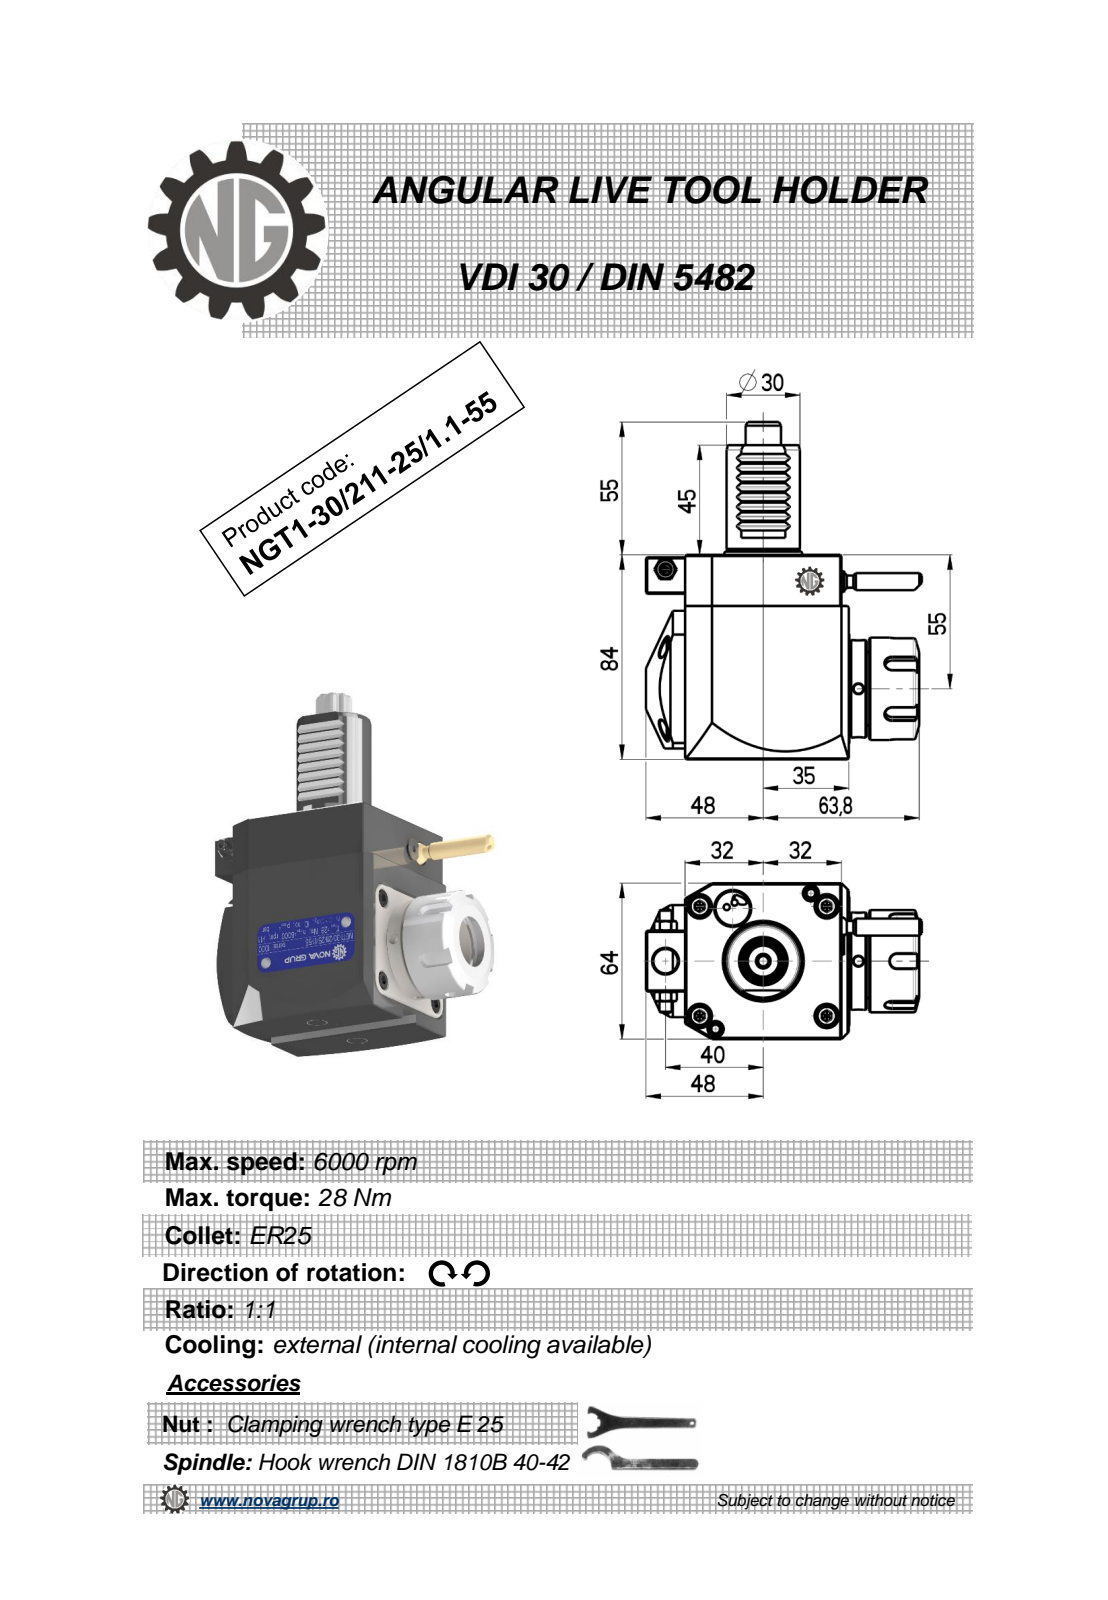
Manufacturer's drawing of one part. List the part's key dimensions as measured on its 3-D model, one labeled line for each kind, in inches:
Part name (STEP PRODUCT): NGT1_30_211_25_1_1_55
STEP written by: PRO/ENGINEER BY PARAMETRIC TECHNOLOGY CORPORATION, 2010280 (CONFIG_CONTROL_DESIGN)
Units: inches
Bodies: 1 solid, 451 faces (176 planar, 118 cylindrical, 157 other)
Overall size (bounding box): 5.472 × 4.444 × 2.583
Volume: 27.11 in³ · Surface area: 70.28 in²
Round holes (diameter × count): ⌀0.157 ×2, ⌀0.165 ×2, ⌀0.098 ×1, ⌀0.118 ×1, ⌀0.374 ×1, ⌀0.394 ×1, ⌀0.799 ×1
Round bosses / shafts (diameter × count): ⌀0.353 ×2, ⌀0.197 ×2, ⌀1.654 ×1, ⌀1.575 ×1, ⌀1.299 ×1, ⌀1.181 ×1, ⌀0.276 ×1
Partial cylindrical surfaces — rounded edges, fillets, slot ends (radius × count): R0.115 ×16, R0.01 ×12, R0.012 ×8, R0.118 ×5, R0.138 ×4, R6.299 ×2, R0.224 ×1, R0.285 ×1
Main face-to-face distances: 2.52, 3.307, 2.646, 0.126, 2.638, 0.118, 3.15, 3.268, 0.63, 0.02
Hole centre spacings: 0.56, 1.533, 1.575, 1.818, 1.831, 3.108, 3.658
